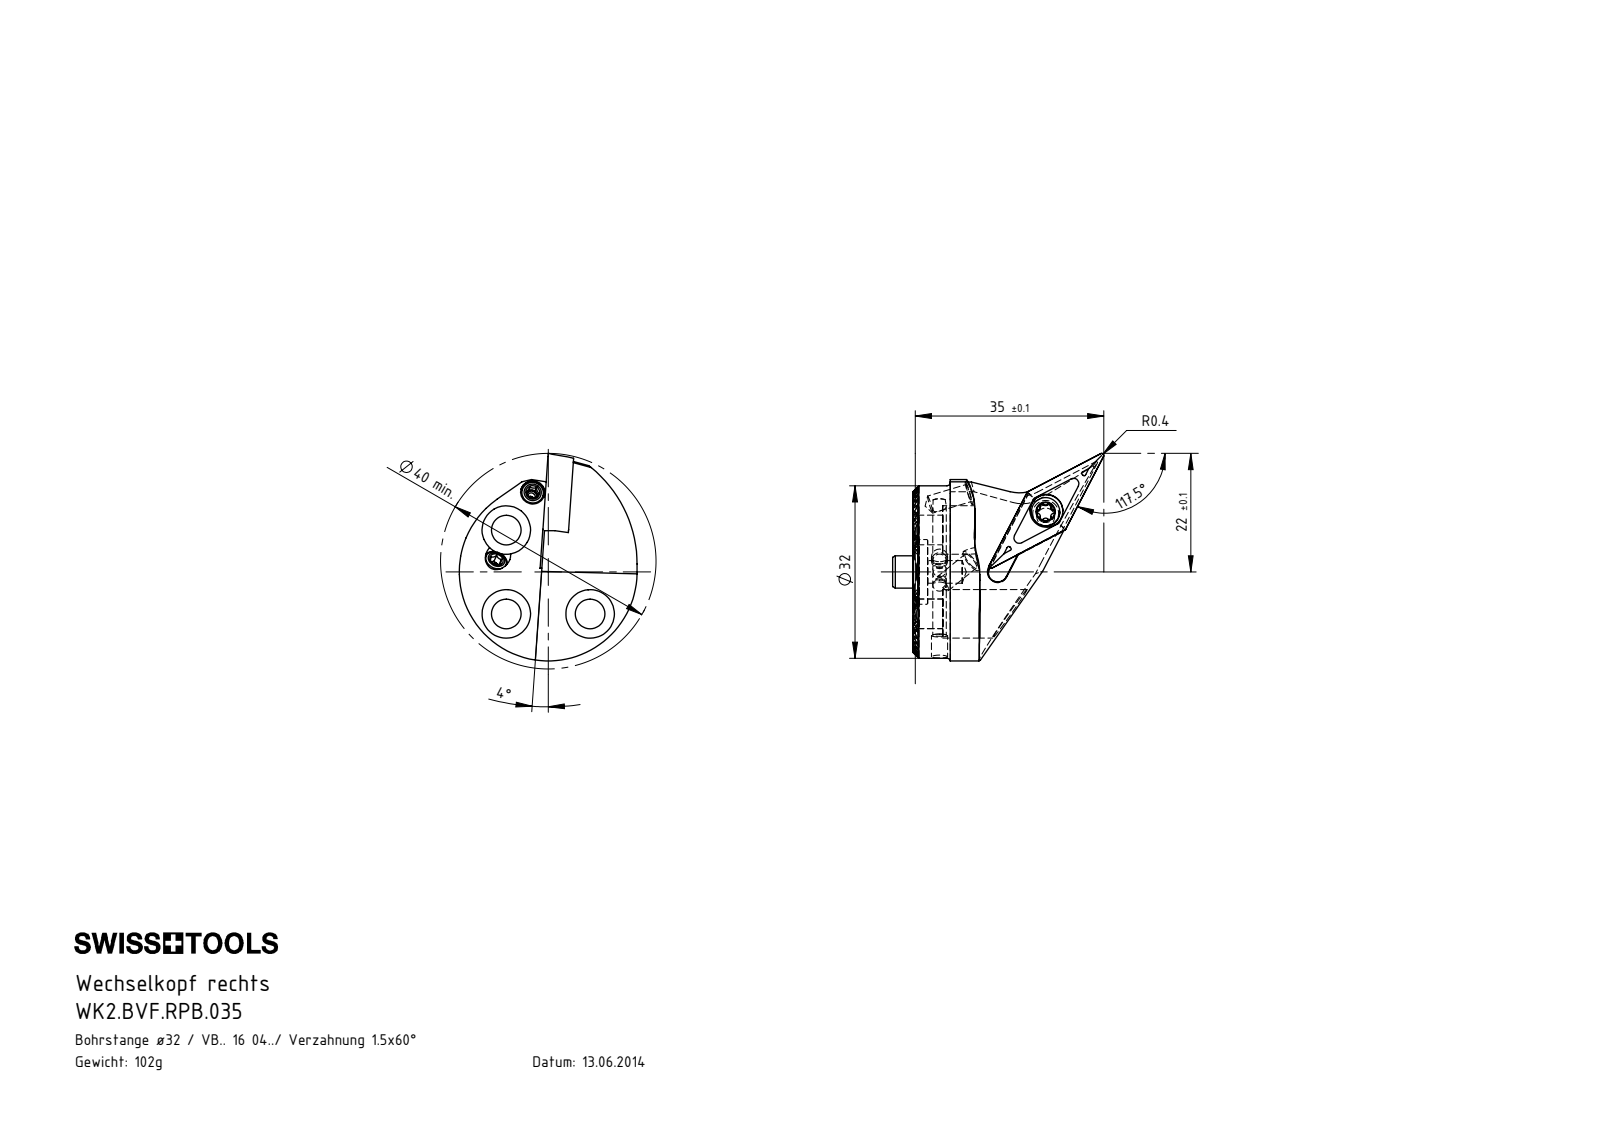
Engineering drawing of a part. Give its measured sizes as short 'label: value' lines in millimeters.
name: WK2-ER1.001.012_A_Fertigbearbeitung; WCB-ER2.001.009_A; WK2-BVF.RPB.035_A_Fertigbearbeitung; KVT_MB_600_030 (+3 more)
written by: SolidWorks 2017 (AUTOMOTIVE_DESIGN)
unit: mm
bodies: 10 solids, 389 faces (201 planar, 101 cylindrical, 87 other)
size: 39.2 × 38.5 × 33
volume: 12 523 mm³; area: 7 534 mm²
holes: 3× ⌀3.3, 3× ⌀5.5, 3× ⌀9, 2× ⌀1.7, 2× ⌀2.38, 2× ⌀2.5, 2× ⌀4.5, 1× ⌀3, 1× ⌀4.2, 1× ⌀4.4, 1× ⌀6.1, 1× ⌀12
bosses: 3× ⌀4, 2× ⌀3, 1× ⌀32, 1× ⌀6, 1× ⌀5.25
rounds: 22× R0.12, 6× R0.34, 6× R0.59, 3× R12, 2× R0.15, 1× R1.75, 1× R7, 1× R16.5
face distances: 1.3, 2.6, 3.9, 5.2, 6.5, 12.99, 11.69, 14.29, 7.8, 10.39
hole spacings: 11, 15.56, 22.01
